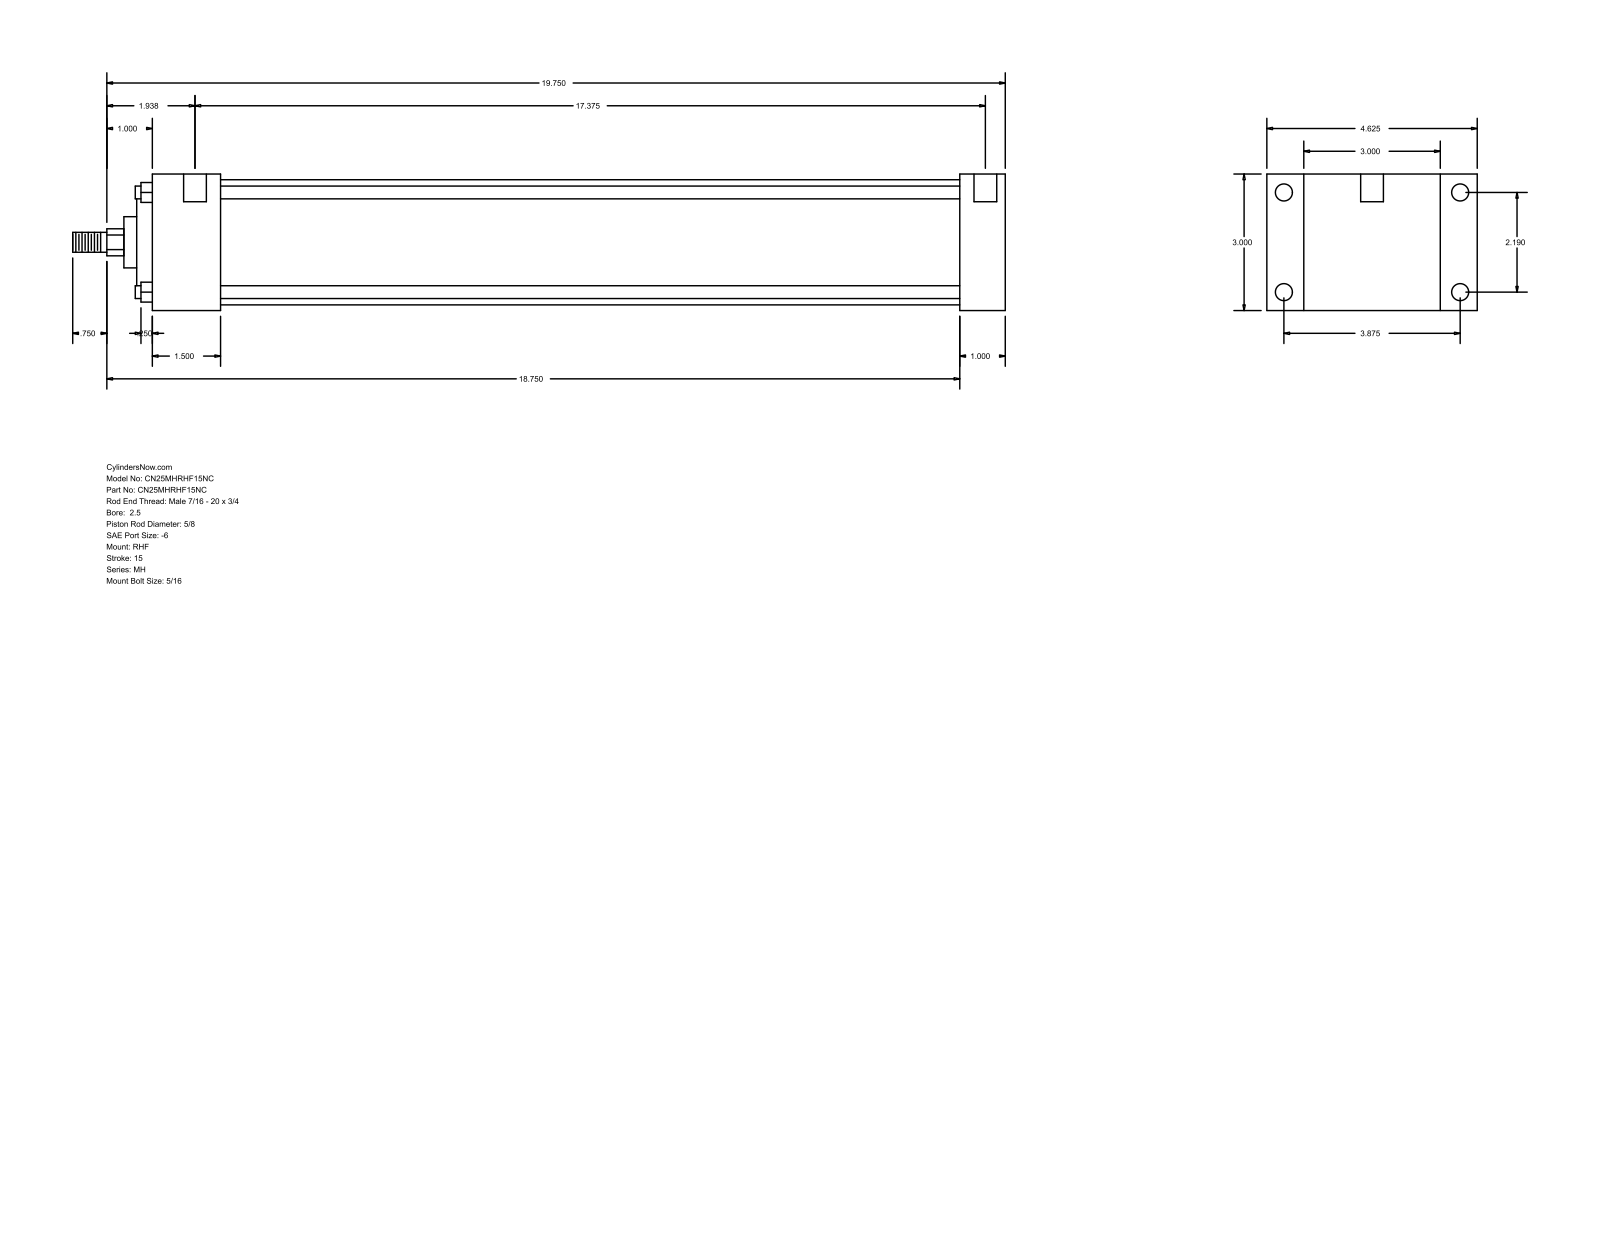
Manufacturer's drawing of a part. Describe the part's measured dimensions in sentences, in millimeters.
The part is named "MH_RHF__0250_0.625". Its 3-D file was written by "GSSL Pune (CONFIG_CONTROL_DESIGN)". It is 0 solids with 90 faces: 61 planar, 29 cylindrical and 0 other. Overall it measures 520.7 by 117.47 by 76.2 millimeters. Round holes: 4 of diameter 5.56, 4 of diameter 9.53, 2 of diameter 12.7. Round bosses or shafts: 4 of diameter 7.14, 1 of diameter 69.85, 1 of diameter 55.55, 1 of diameter 28.57, 1 of diameter 15.88, 1 of diameter 11.11. Partial cylindrical surfaces (rounded edges, fillets, slot ends): 1 of radius 7.54. The main face-to-face distances are 76.2, 25.4, 20.64, 96.84, 476.25, 450.85, 38.1, 117.48, 412.75, 438.15. The hole center spacings are 55.62, 98.42, 113.05, 449.26, 3.17, 4.76, 441.33, 444.5.
